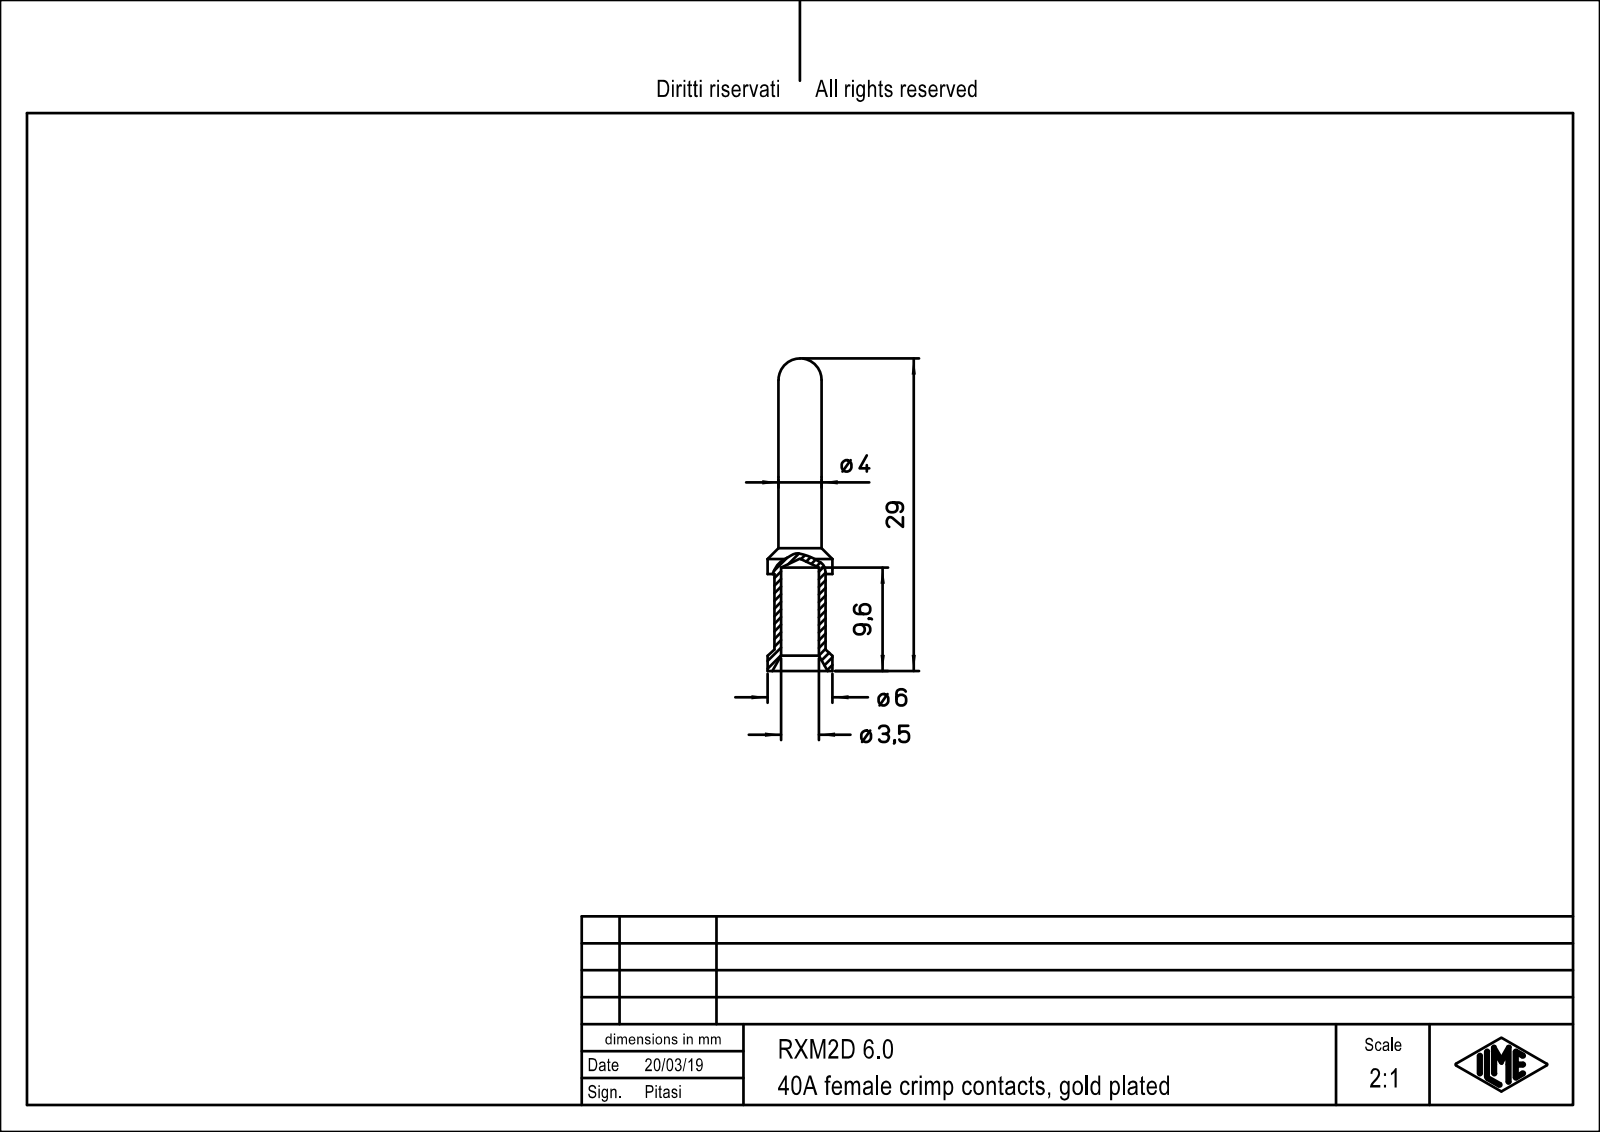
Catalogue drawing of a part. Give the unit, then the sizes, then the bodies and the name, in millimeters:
Units: millimetres
Overall size (bounding box): 29 × 6 × 6
Round holes (diameter × count): ⌀3.5 ×1
Round bosses / shafts (diameter × count): ⌀6 ×1, ⌀5 ×1, ⌀4 ×1
Main face-to-face distances: 9.6
Volume: 376 mm³ · Surface area: 558 mm²
Bodies: 1 solid, 24 faces (2 planar, 12 cylindrical, 10 other)
Part name (STEP PRODUCT): RXM2D_6-0
STEP written by: PTC Creo Elements/Direct Modeling 19.0E 27-Jun-2016 (C) Parametric Technology GmbH (AUTOMOTIVE_DESIGN)
